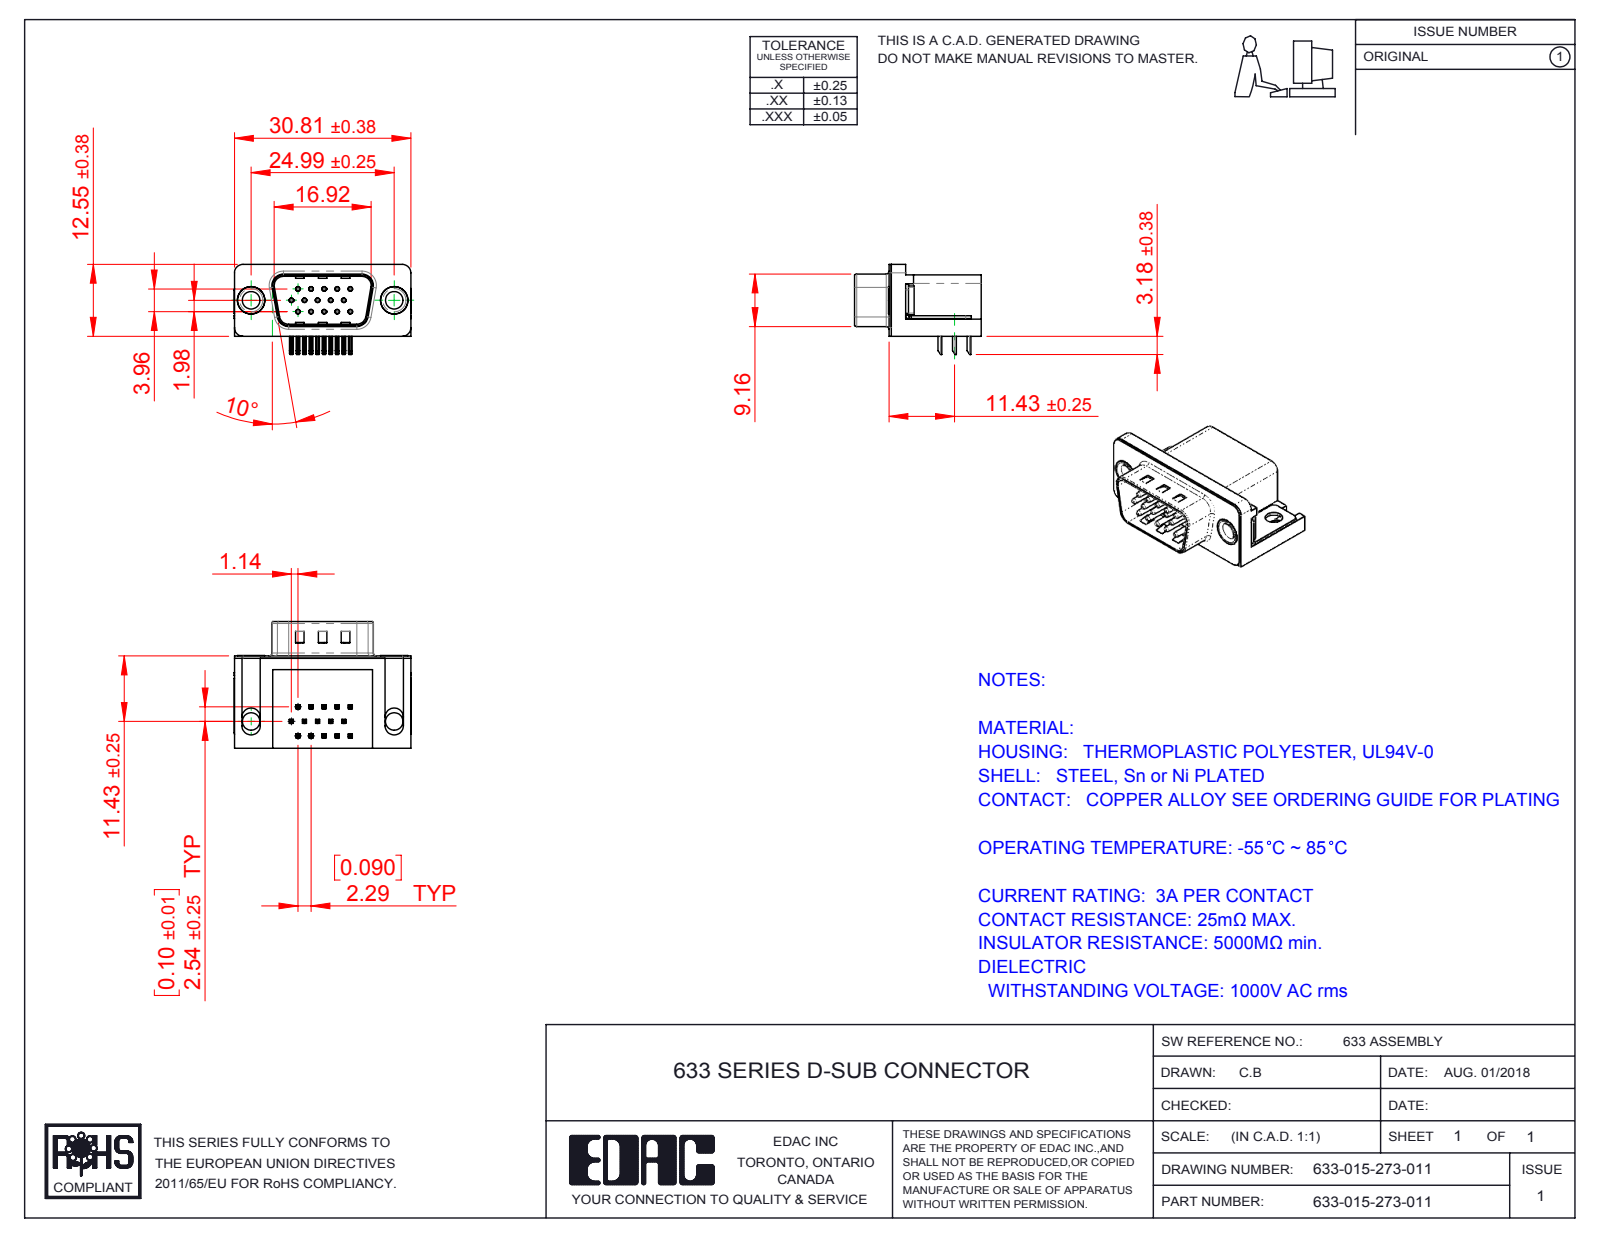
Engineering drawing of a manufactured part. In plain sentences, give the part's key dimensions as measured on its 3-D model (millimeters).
The part is named "633 Thru Hole Rivet; 633 Shell_15 Contact; 633-015-273-011; 633 Housing_15 Contact (+5 more)". Its 3-D file was written by "SolidWorks 2016 (CONFIG_CONTROL_DESIGN)". It is 21 solids with 1401 faces: 859 planar, 425 cylindrical and 117 other. Overall it measures 30.89 by 22.1 by 15.73 millimeters. Its volume is 4 060 cubic millimeters and its surface area 5 390 square millimeters. Round holes: 15 of diameter 0.35, 15 of diameter 0.8, 4 of diameter 3.05, 2 of diameter 4, 2 of diameter 4.8, 2 of diameter 5. Round bosses or shafts: 15 of diameter 0.75, 2 of diameter 4.9, 2 of diameter 4.75, 2 of diameter 3.85. Partial cylindrical surfaces (rounded edges, fillets, slot ends): 68 of radius 0.25, 30 of radius 0.12, 16 of radius 1, 9 of radius 0.5, 8 of radius 1.6, 7 of radius 1.5, 4 of radius 0.9, 4 of radius 2. The main face-to-face distances are 0.4, 10.35, 15.7, 0.5, 2.9, 2.5, 6.7, 16.1, 0.35, 10.7. The hole center spacings are 3.96, 2.28, 4.57, 2.29, 6.05, 6.86, 7.92, 6.04.
